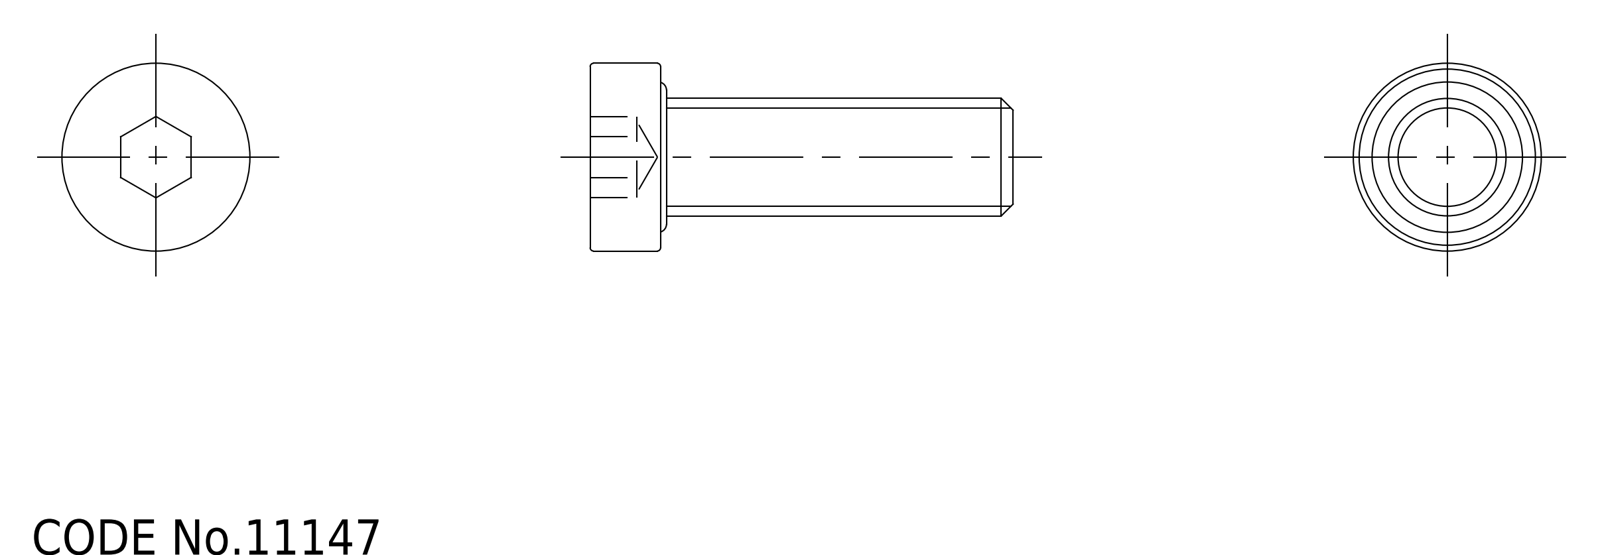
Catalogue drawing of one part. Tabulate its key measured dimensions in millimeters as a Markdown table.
| quantity | value |
| --- | --- |
| part name | screw; TL_418_M10_30 |
| STEP written by | SolidWorks 2015 (AUTOMOTIVE_DESIGN) |
| units | millimeters |
| bodies | 2 solids, 27 faces (11 planar, 6 cylindrical, 10 other) |
| overall size | 36 × 16 × 16 |
| volume | 3 388 mm³ |
| surface area | 1 925 mm² |
| round holes (diameter × count) | 15 × 1 |
| round bosses / shafts (diameter × count) | 16 × 1, 10 × 1 |
| main face-to-face distances | 5.1, 6, 36, 30.9, 4, 1.1, 32, 2, 0.9, 30 |
